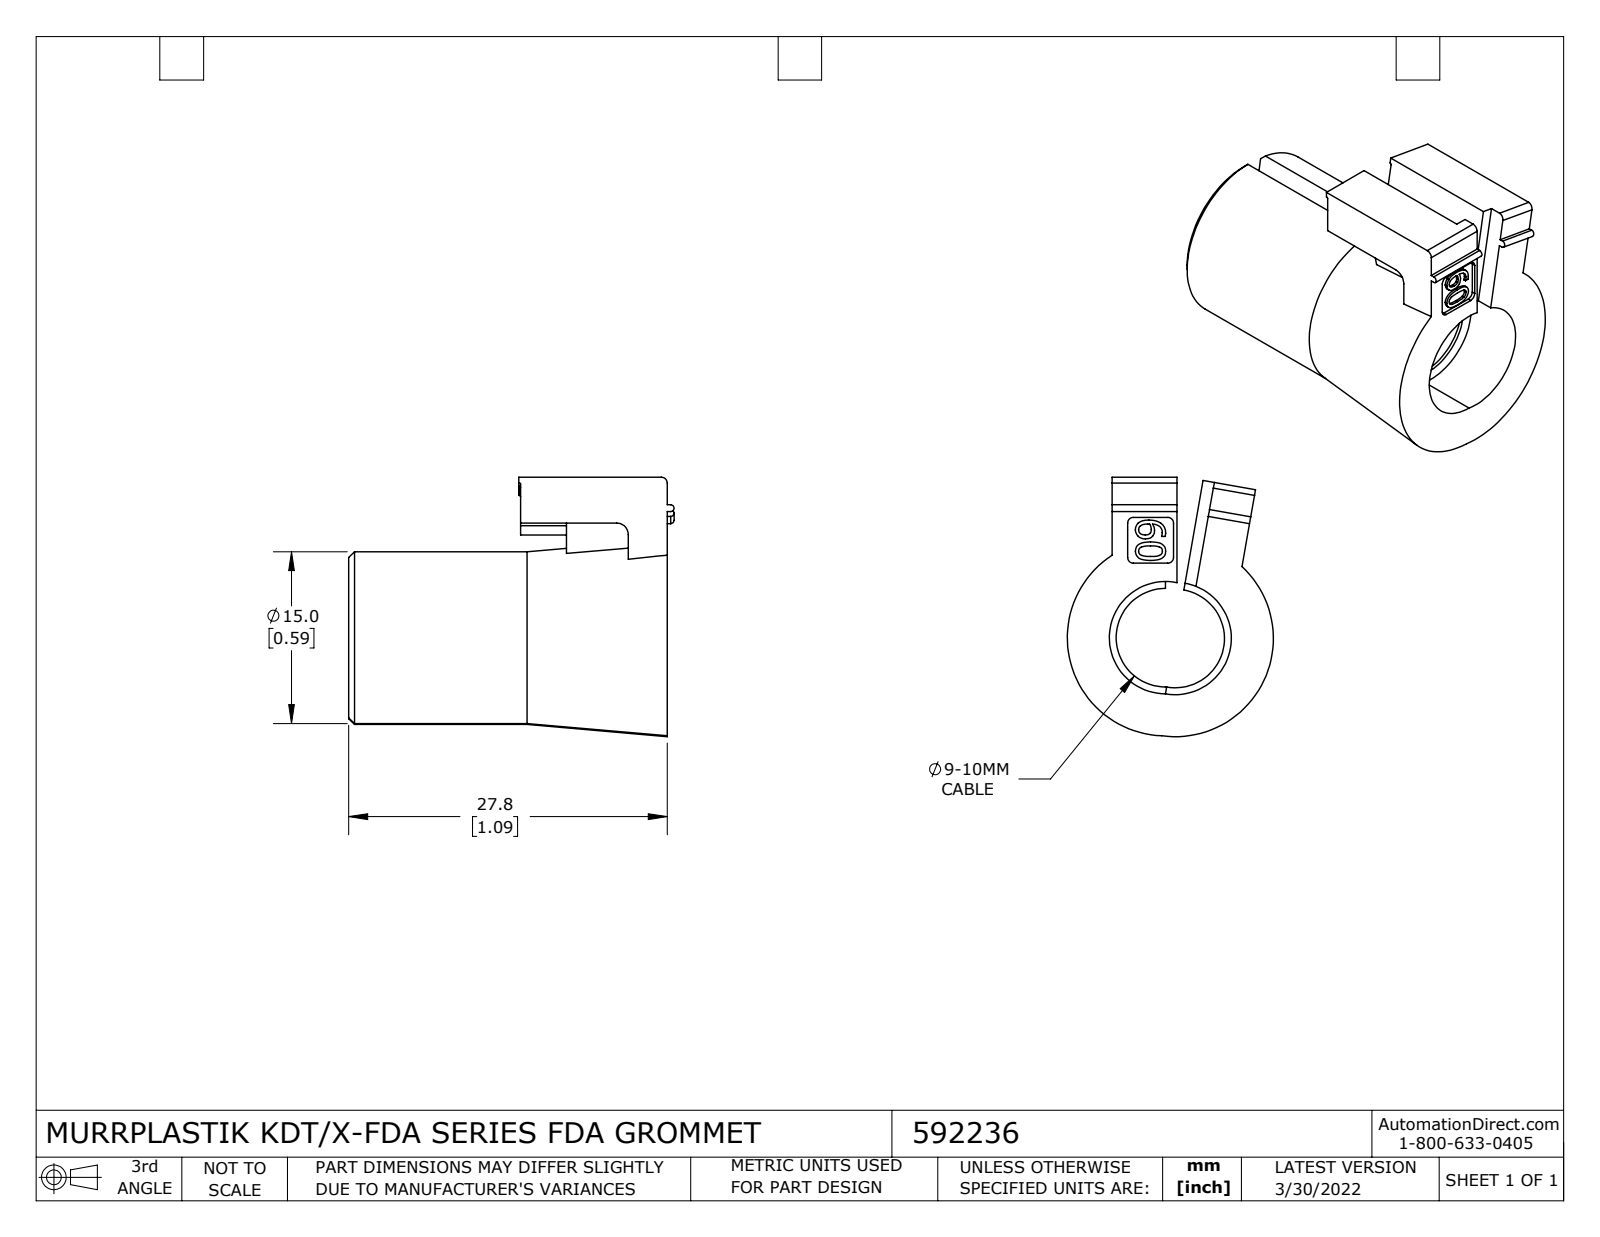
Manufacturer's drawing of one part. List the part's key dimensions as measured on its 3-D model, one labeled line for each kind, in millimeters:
Part name (STEP PRODUCT): 592236
STEP written by: SolidWorks 2021 (CONFIG_CONTROL_DESIGN)
Units: millimetres
Bodies: 1 solid, 111 faces (44 planar, 24 cylindrical, 43 other)
Overall size (bounding box): 28.4 × 22.6 × 18
Volume: 3 740 mm³ · Surface area: 3 158 mm²
Partial cylindrical surfaces — rounded edges, fillets, slot ends (radius × count): R0.5 ×6, R0.1 ×2, R0.3 ×2, R1 ×2, R4.3 ×2, R4.9 ×2, R7.5 ×2
Main face-to-face distances: 4.6, 27.8, 4, 12.8, 15, 1, 1.5, 11.3, 26.3, 5.6
